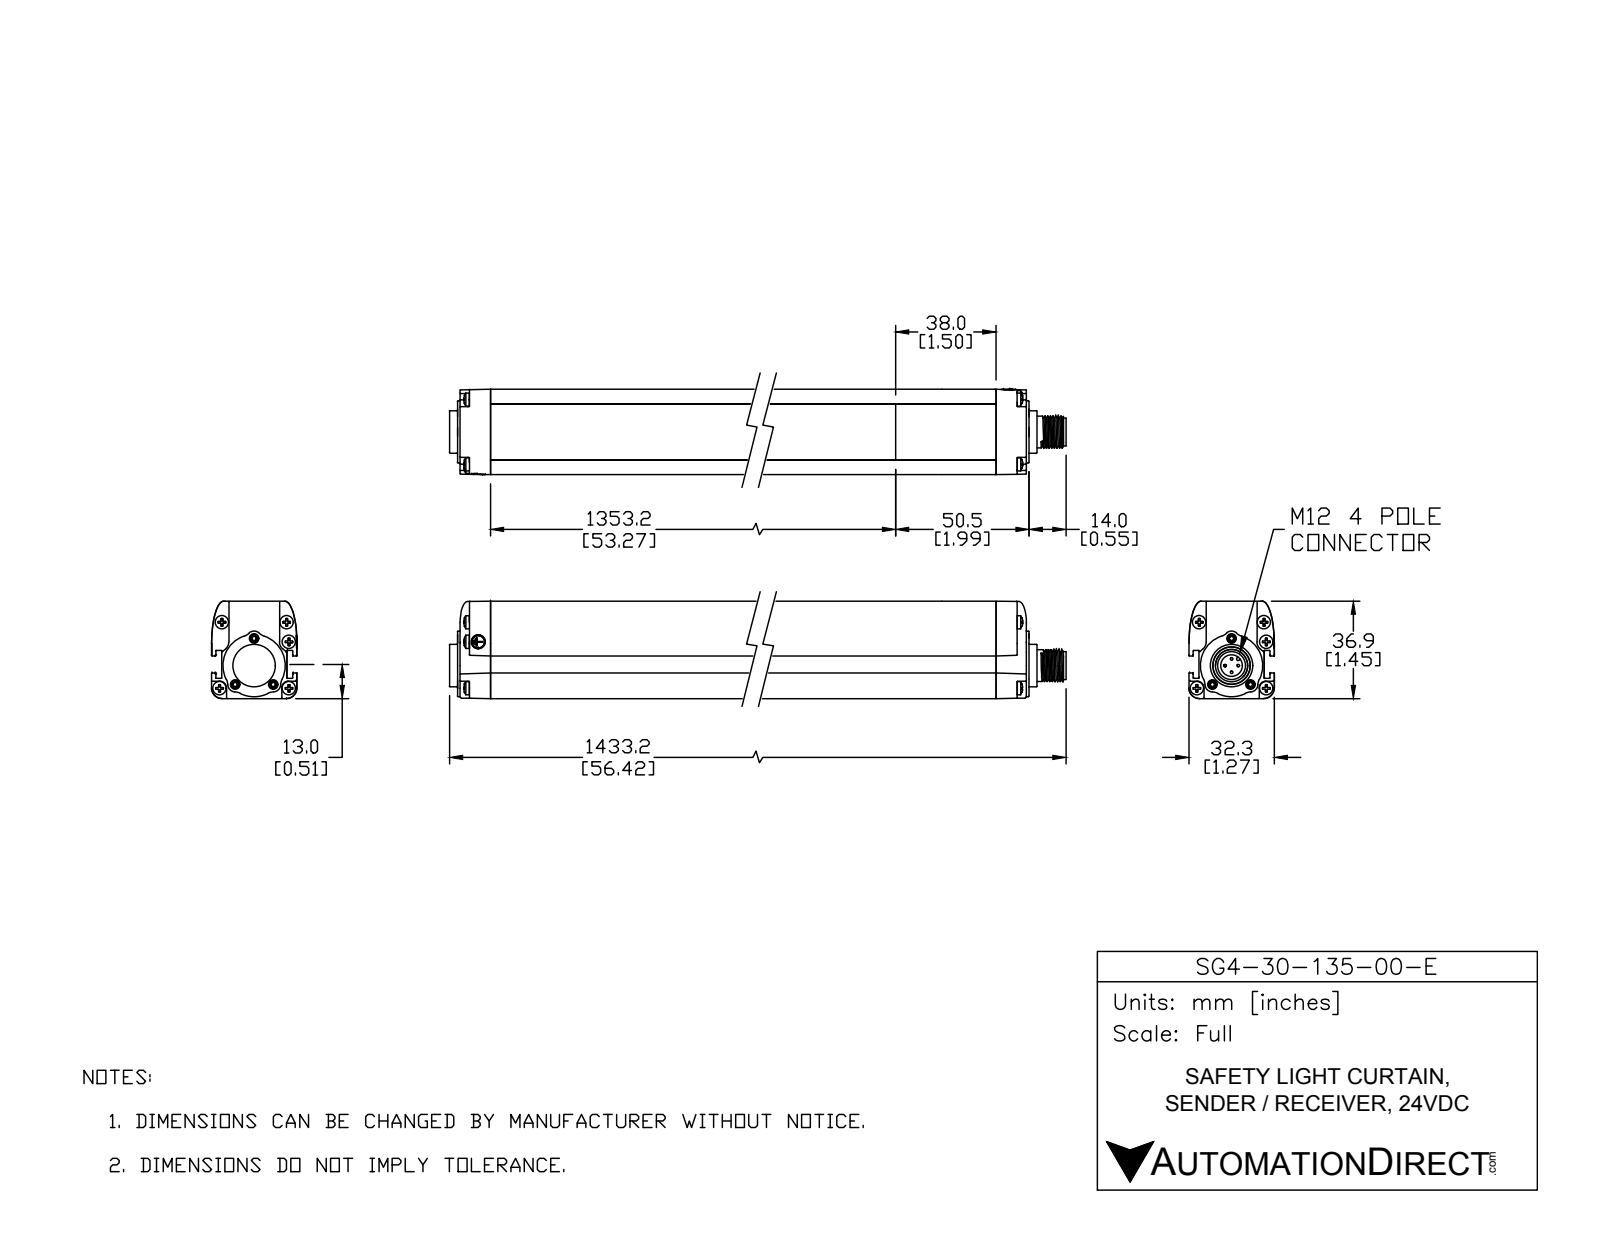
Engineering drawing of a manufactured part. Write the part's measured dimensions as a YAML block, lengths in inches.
part_name: "SG4-30-135-OO-E"
step_written_by: "SolidWorks 2017 (AUTOMOTIVE_DESIGN)"
units: inches
bodies: {solids: 29, faces: 1674, planar: 410, cylindrical: 591, other: 673}
overall_size: [56.425, 2.48, 2.055]
volume: 90.01
surface_area: 538.5
round_holes:
  - {diameter: 0.106, count: 6}
  - {diameter: 0.209, count: 6}
  - {diameter: 0.081, count: 4}
  - {diameter: 0.165, count: 4}
  - {diameter: 0.26, count: 4}
  - {diameter: 0.059, count: 3}
  - {diameter: 0.142, count: 3}
  - {diameter: 0.323, count: 1}
  - {diameter: 0.376, count: 1}
  - {diameter: 0.433, count: 1}
  - {diameter: 0.563, count: 1}
round_bosses_or_shafts:
  - {diameter: 0.197, count: 10}
  - {diameter: 0.394, count: 4}
  - {diameter: 0.039, count: 4}
  - {diameter: 0.185, count: 2}
  - {diameter: 0.63, count: 1}
  - {diameter: 0.55, count: 1}
  - {diameter: 0.472, count: 1}
  - {diameter: 0.413, count: 1}
partial_cylinders:
  - {radius: 0.008, count: 148}
  - {radius: 0.004, count: 120}
  - {radius: 0.006, count: 18}
  - {radius: 0.106, count: 18}
  - {radius: 0.118, count: 8}
  - {radius: 0.197, count: 7}
  - {radius: 0.11, count: 3}
  - {radius: 0.016, count: 2}
face_to_face_distances: [0.079, 1.272, 1.429, 0.15, 1.122, 1.35, 0.157, 0.972, 0.333, 0.063]
hole_center_spacings: [0.569, 53.197, 0.402, 0.24, 0.293, 0.52, 0.541, 0.619]
